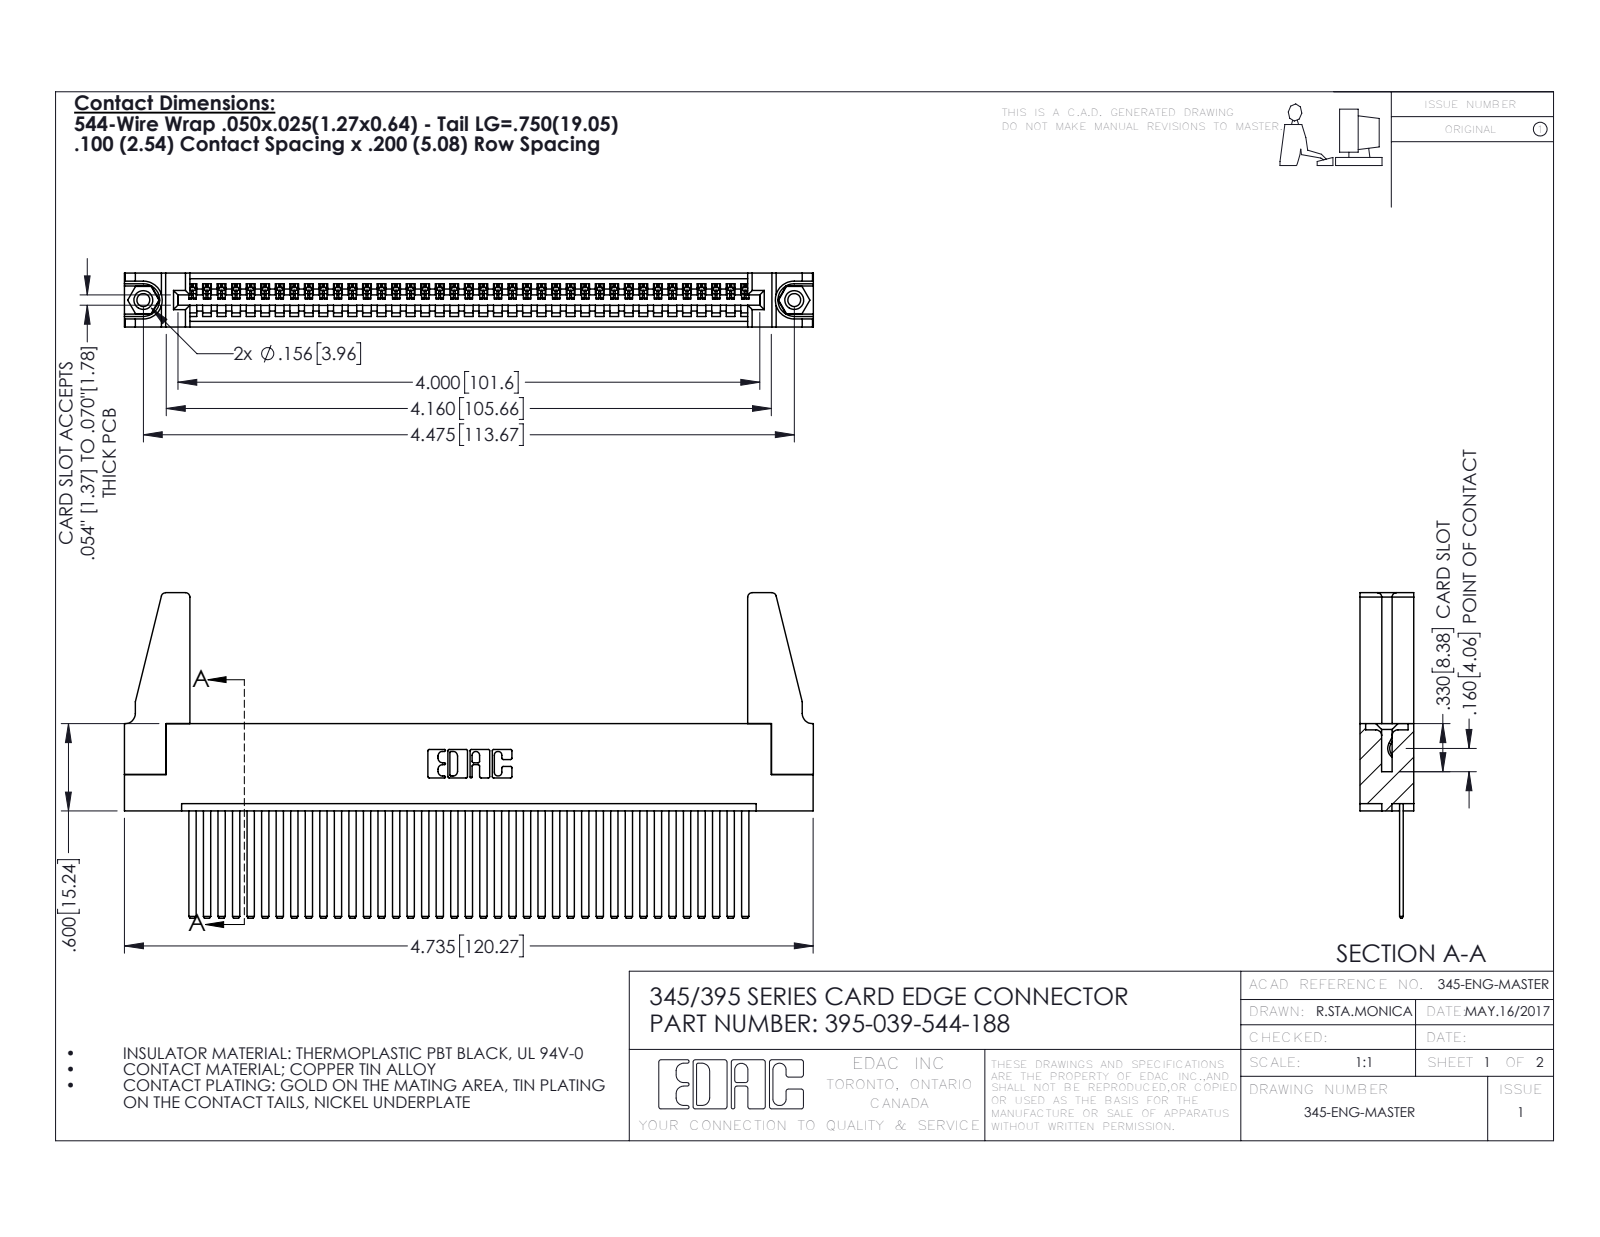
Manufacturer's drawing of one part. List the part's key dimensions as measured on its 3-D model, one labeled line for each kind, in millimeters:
Part name (STEP PRODUCT): 345-292-001_345-293-144; 395-039-544-188; 345-250-001_345-250-001-102; 345 Part_Flush Mounting Lugs - 0.156 Dia-TH (+1 more)
STEP written by: SolidWorks 2016 (CONFIG_CONTROL_DESIGN)
Units: millimetres
Bodies: 44 solids, 2278 faces (1556 planar, 706 cylindrical, 16 other)
Overall size (bounding box): 120.3 × 56.8 × 9.4
Volume: 15 100 mm³ · Surface area: 20 190 mm²
Round holes (diameter × count): ⌀2.3 ×2, ⌀3.2 ×2, ⌀4 ×2, ⌀1.6 ×1
Round bosses / shafts (diameter × count): ⌀3.9 ×2
Partial cylindrical surfaces — rounded edges, fillets, slot ends (radius × count): R0.2 ×78, R0.3 ×22, R0.8 ×8, R0.2 ×6, R0.8 ×6, R0.7 ×3, R0.8 ×2, R1 ×2
Main face-to-face distances: 1.8, 7.6, 2.5, 6.9, 0.6, 9.4, 5.1, 5.7, 3.8, 1.8
Hole centre spacings: 6.9, 107.7, 113.7
